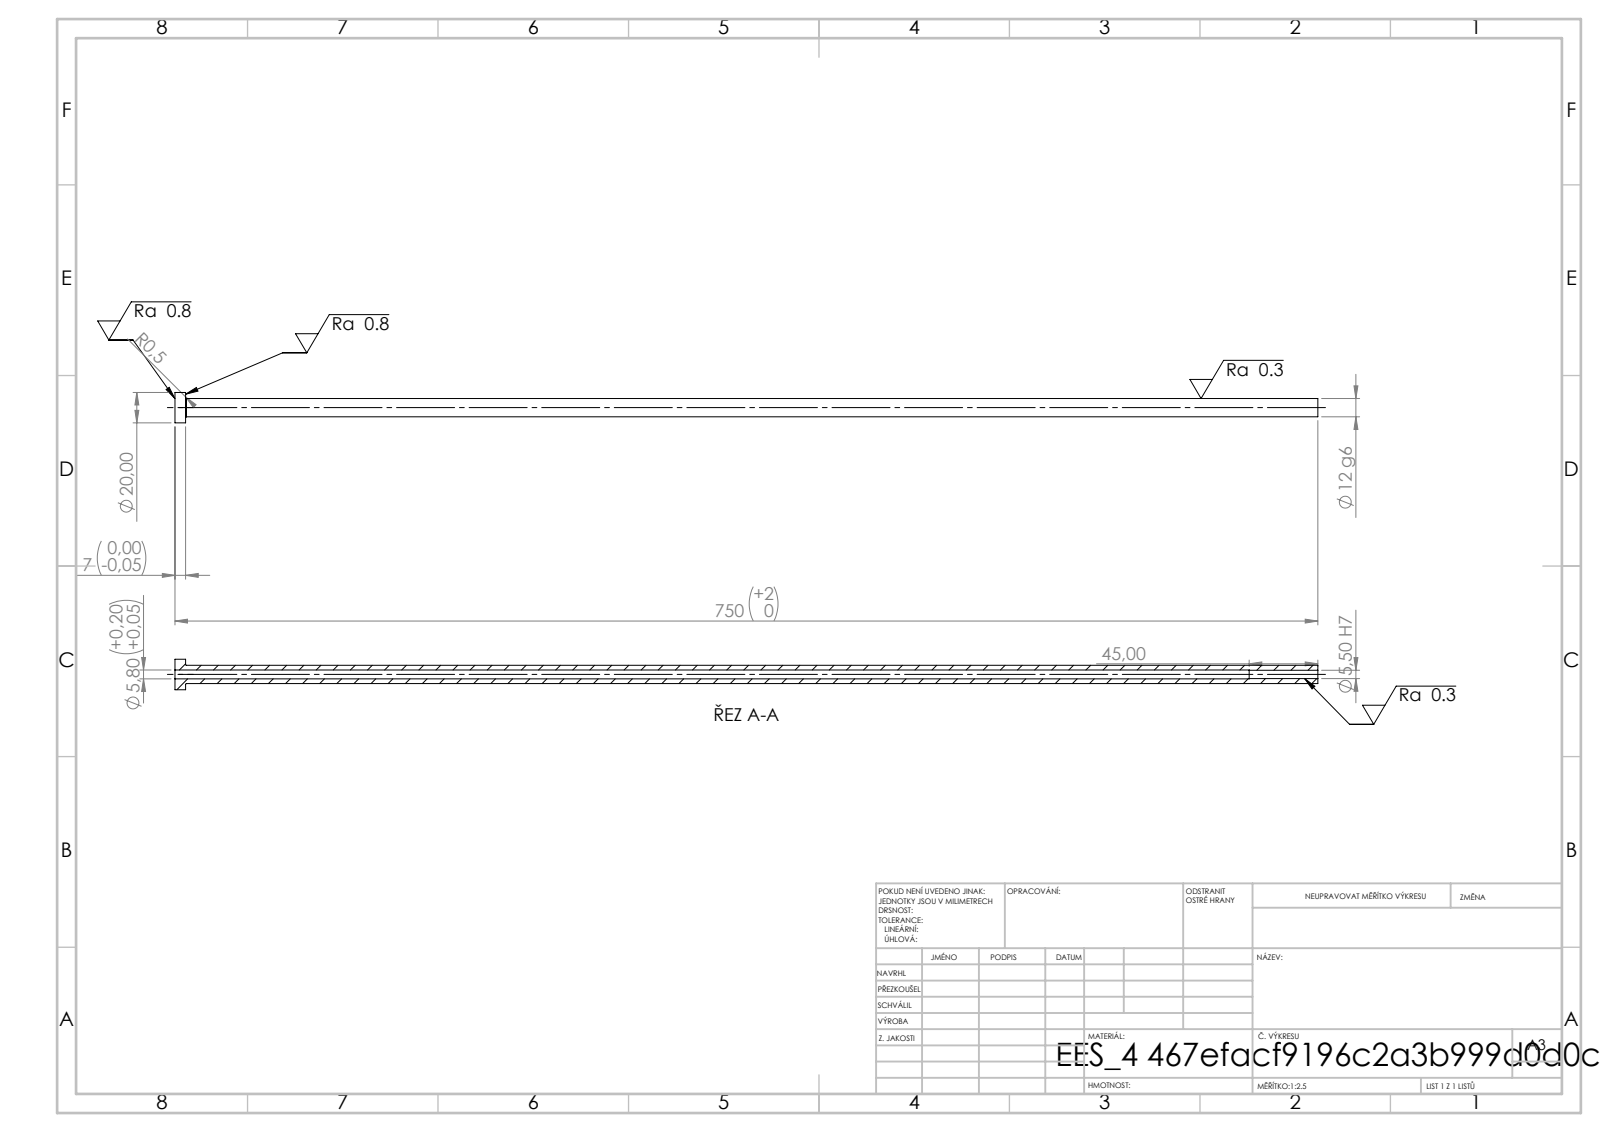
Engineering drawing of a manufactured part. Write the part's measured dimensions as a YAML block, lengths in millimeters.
step_written_by: "SolidWorks 2019 (CONFIG_CONTROL_DESIGN)"
units: millimeters
bodies: {solids: 1, faces: 14, planar: 4, cylindrical: 8, other: 2}
overall_size: [750, 20, 20]
volume: 66537
surface_area: 42647
round_holes:
  - {diameter: 5.5, count: 1}
  - {diameter: 5.8, count: 1}
round_bosses_or_shafts:
  - {diameter: 20, count: 1}
  - {diameter: 12, count: 1}
face_to_face_distances: [7, 750, 743, 705, 698, 45]
